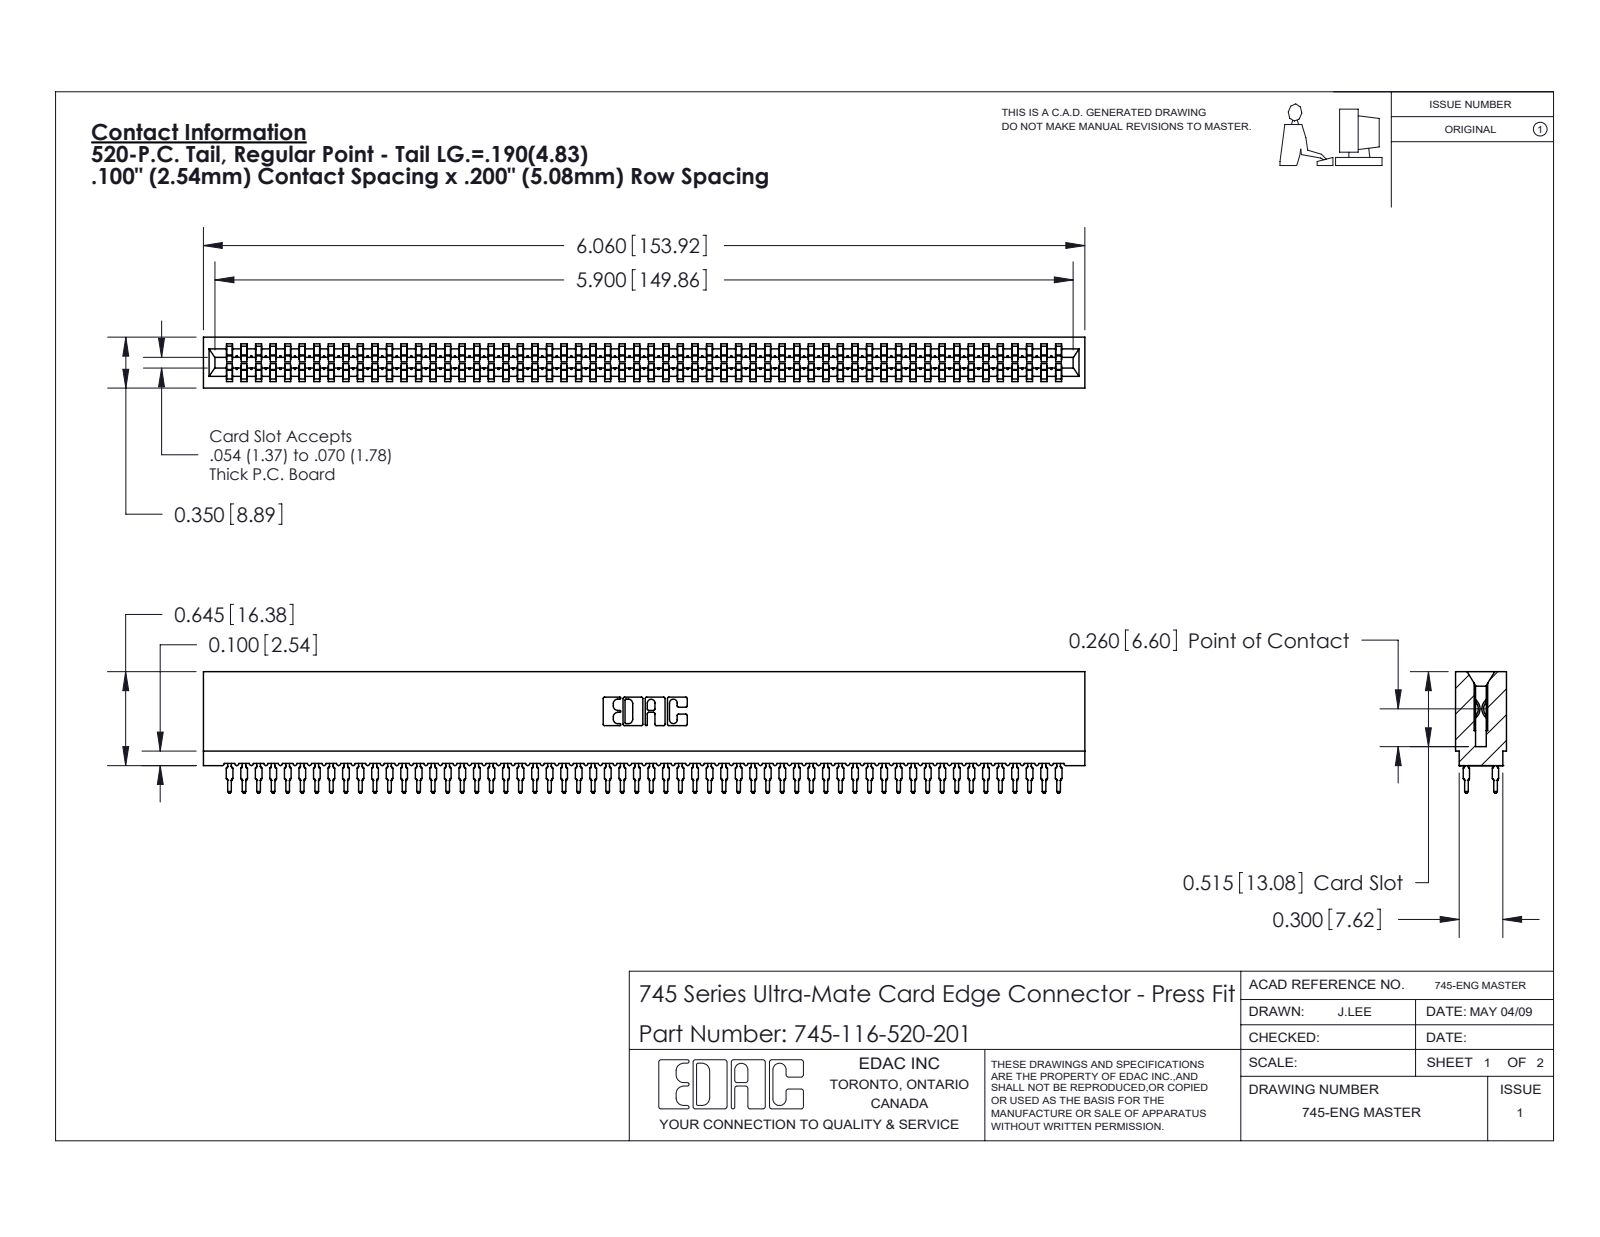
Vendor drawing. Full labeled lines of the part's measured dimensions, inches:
Part name (STEP PRODUCT): 745-116-520-201; 745 Part_Insulator Option - 01; 745-292-001_520
STEP written by: SolidWorks 2020 (CONFIG_CONTROL_DESIGN)
Units: inches
Bodies: 117 solids, 10477 faces (5391 planar, 2070 cylindrical, 3016 other)
Overall size (bounding box): 6.06 × 0.836 × 0.35
Volume: 0.834 in³ · Surface area: 42.81 in²
Partial cylindrical surfaces — rounded edges, fillets, slot ends (radius × count): R0.021 ×232, R0.015 ×116, R0.01 ×22, R0.005 ×8, R0.011 ×8, R0.007 ×6, R0.031 ×6, R0.026 ×3
Main face-to-face distances: 0.35, 0.063, 0.287, 0.045, 0.305, 0.018, 0.243, 0.138, 0.212, 0.093
